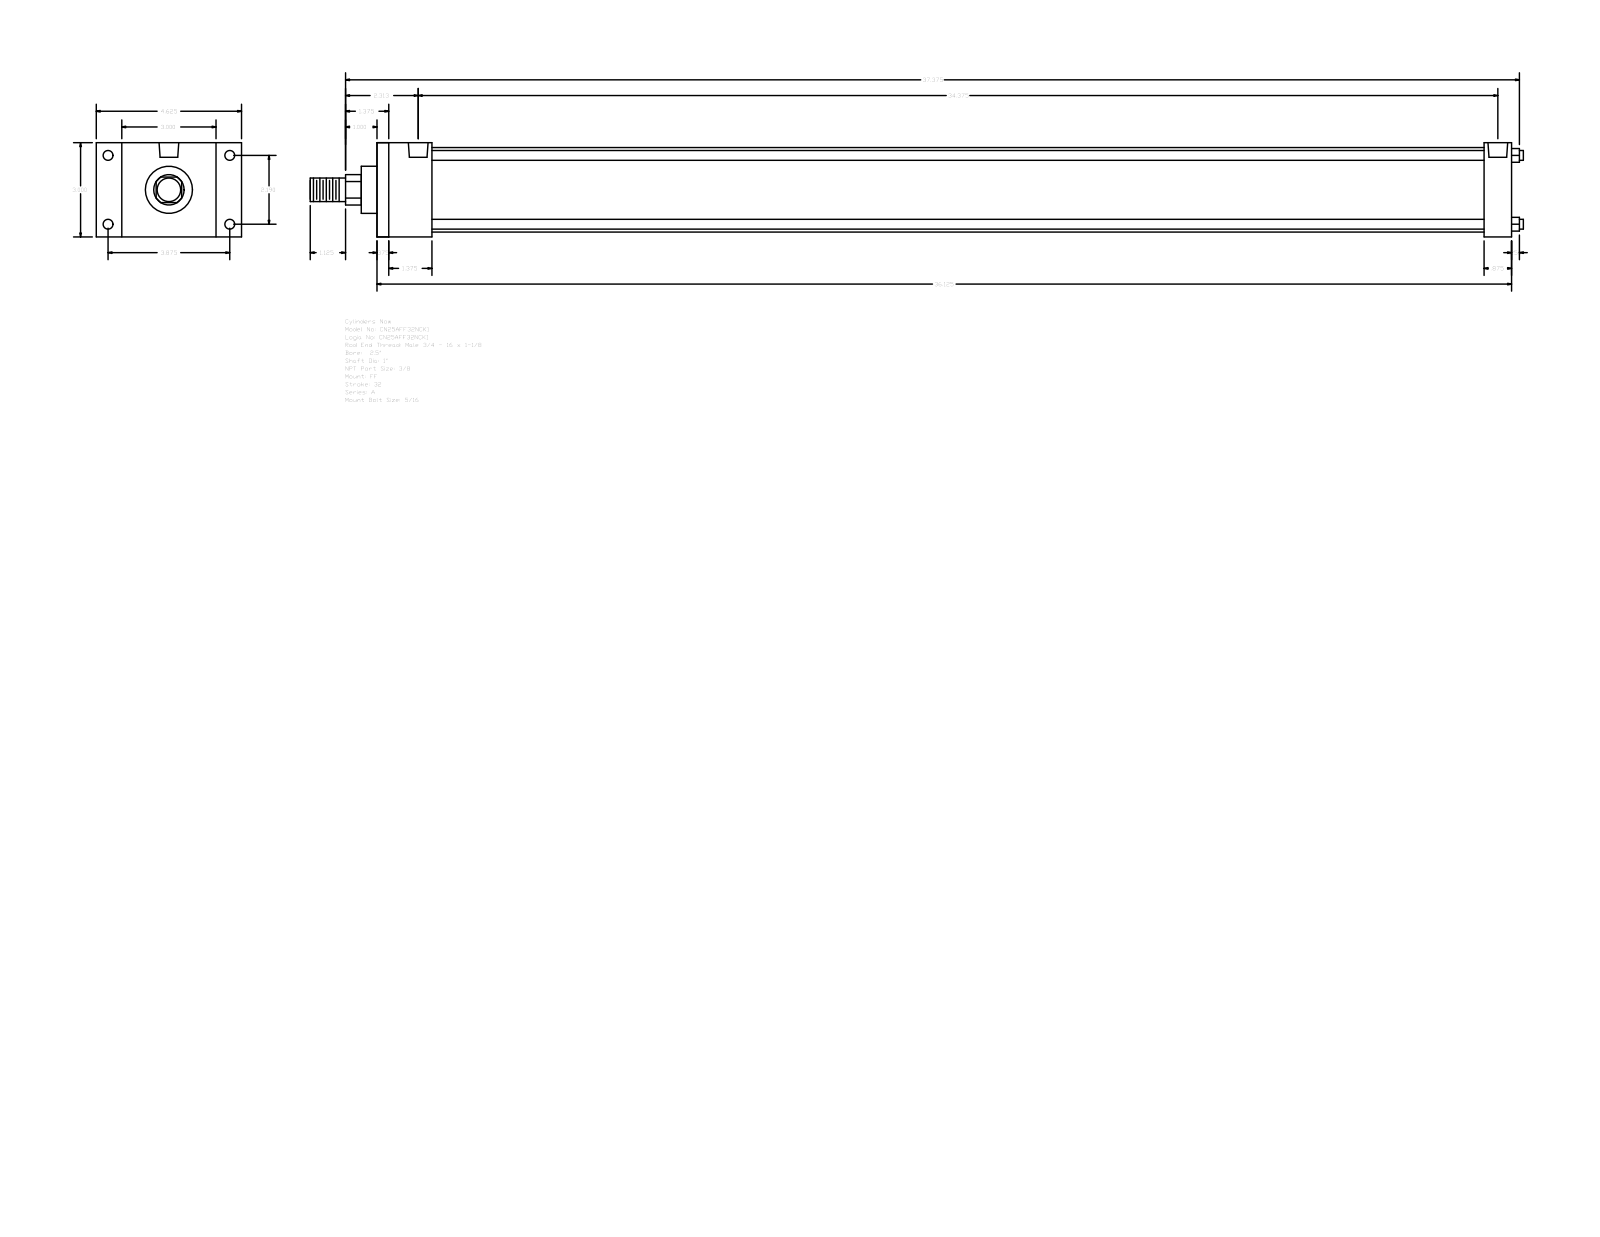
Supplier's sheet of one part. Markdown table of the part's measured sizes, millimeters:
| quantity | value |
| --- | --- |
| part name | A_FF__0250_1 |
| STEP written by | GSSL Pune (CONFIG_CONTROL_DESIGN) |
| units | millimeters |
| bodies | 0 solids, 92 faces (64 planar, 28 cylindrical, 0 other) |
| overall size | 981.08 × 117.47 × 76.2 |
| round holes (diameter × count) | 5.56 × 4, 7.94 × 4, 15.93 × 2 |
| round bosses / shafts (diameter × count) | 7.94 × 4, 68.33 × 1, 38.1 × 1, 25.4 × 1, 19.05 × 1 |
| partial cylindrical surfaces (radius × count) | 12.29 × 1 |
| main face-to-face distances | 76.2, 917.58, 9.52, 908.06, 44.45, 895.35, 34.93, 885.83, 850.9, 873.13 |
| hole center spacings | 2.38, 55.62, 98.42, 113.05, 875.5, 877.88, 873.12 |
